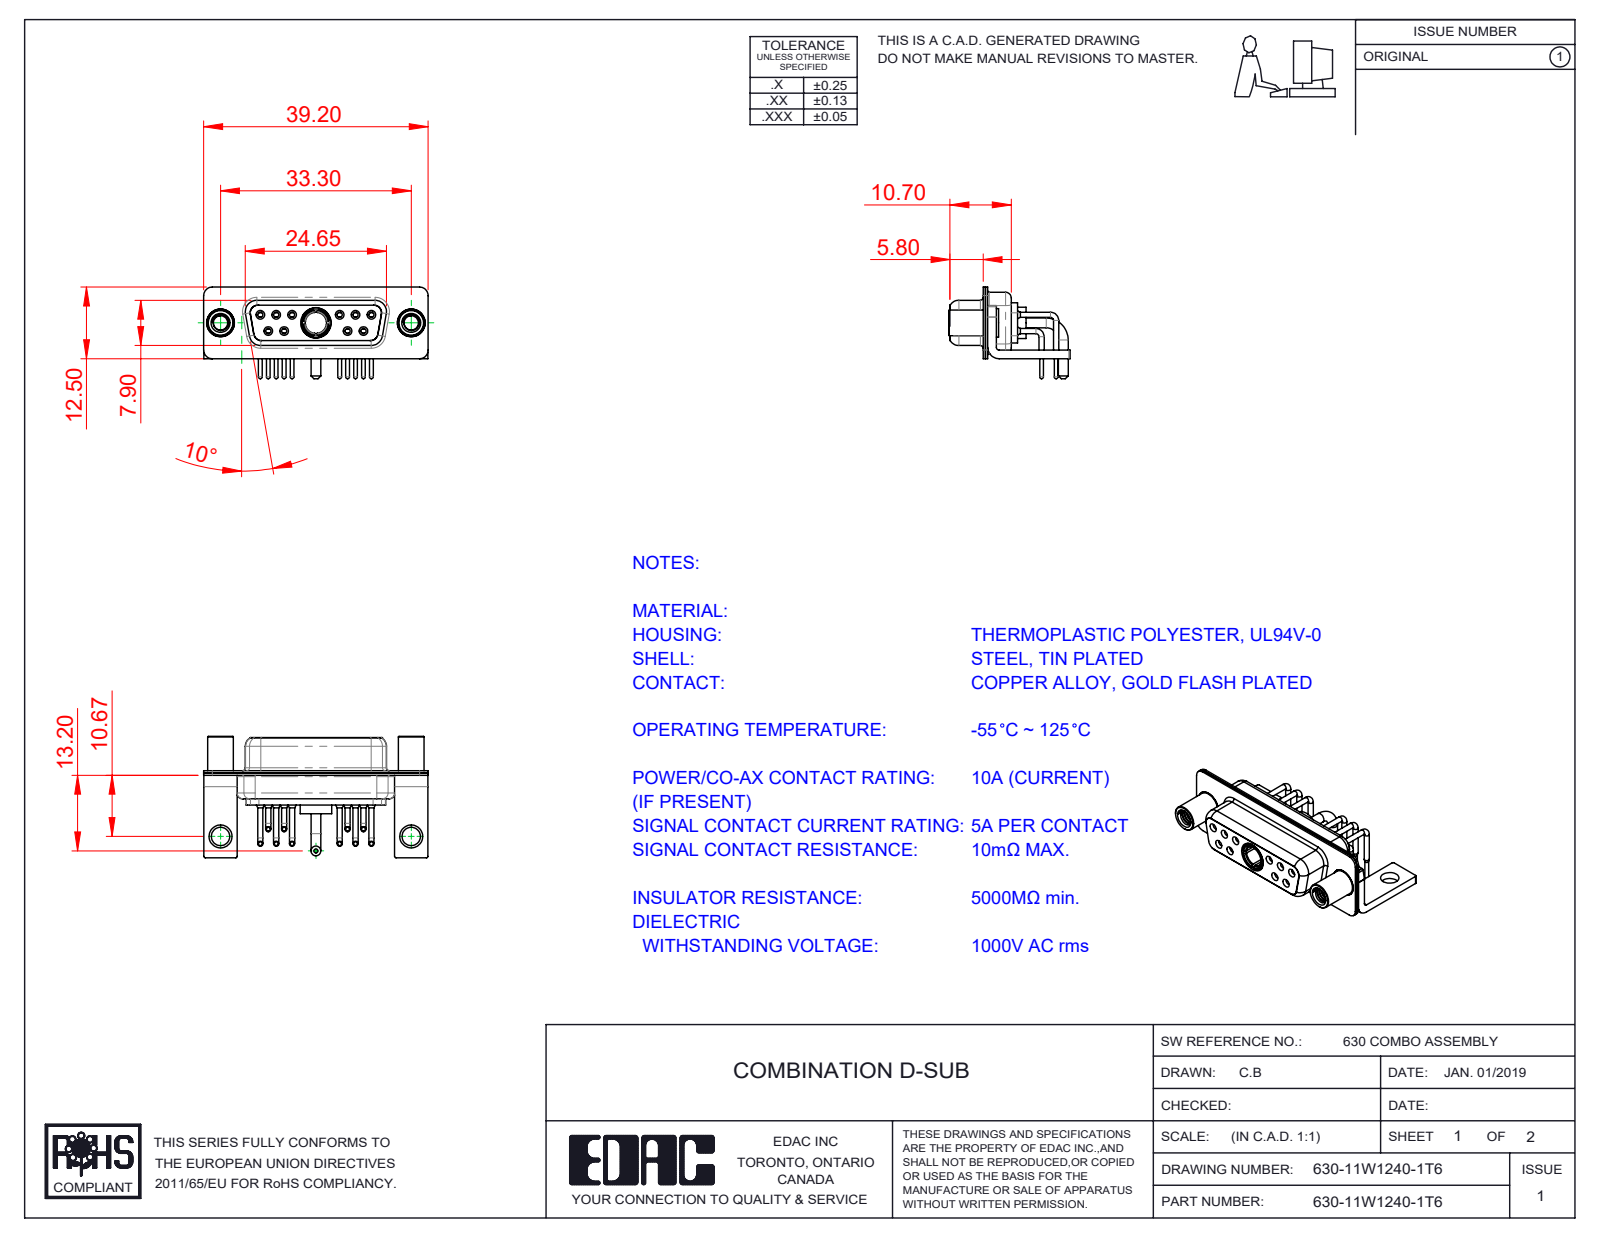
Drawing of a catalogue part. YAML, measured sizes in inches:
part_name: "630Combo Contact Row 1; 630Combo Threaded Standoff_D; 630Combo Contact Row 2; 630Combo Housing_11W1 (+5 more)"
step_written_by: "SolidWorks 2020 (CONFIG_CONTROL_DESIGN)"
units: inches
bodies: {solids: 19, faces: 985, planar: 268, cylindrical: 464, other: 253}
overall_size: [1.543, 0.835, 0.63]
volume: 0.181
surface_area: 11.08
round_holes:
  - {diameter: 0.035, count: 10}
  - {diameter: 0.043, count: 10}
  - {diameter: 0.059, count: 10}
  - {diameter: 0.079, count: 10}
  - {diameter: 0.067, count: 6}
  - {diameter: 0.063, count: 4}
  - {diameter: 0.191, count: 3}
  - {diameter: 0.098, count: 2}
  - {diameter: 0.126, count: 2}
  - {diameter: 0.157, count: 2}
  - {diameter: 0.159, count: 2}
  - {diameter: 0.146, count: 1}
round_bosses_or_shafts:
  - {diameter: 0.035, count: 10}
  - {diameter: 0.026, count: 10}
  - {diameter: 0.063, count: 6}
  - {diameter: 0.197, count: 2}
  - {diameter: 0.195, count: 2}
  - {diameter: 0.189, count: 2}
  - {diameter: 0.177, count: 2}
  - {diameter: 0.067, count: 2}
partial_cylinders:
  - {radius: 0.01, count: 16}
  - {radius: 0.059, count: 16}
  - {radius: 0.079, count: 13}
  - {radius: 0.053, count: 12}
  - {radius: 0.063, count: 8}
  - {radius: 0.02, count: 5}
  - {radius: 0.024, count: 4}
  - {radius: 0.026, count: 4}
face_to_face_distances: [0.016, 0.031, 0.055, 0.018, 0.333, 0.059, 0.071, 0.35, 0.244, 0.091]
hole_center_spacings: [0.124, 0.109, 0.545, 0.436, 0.654, 0.198, 0.198, 0.218]
